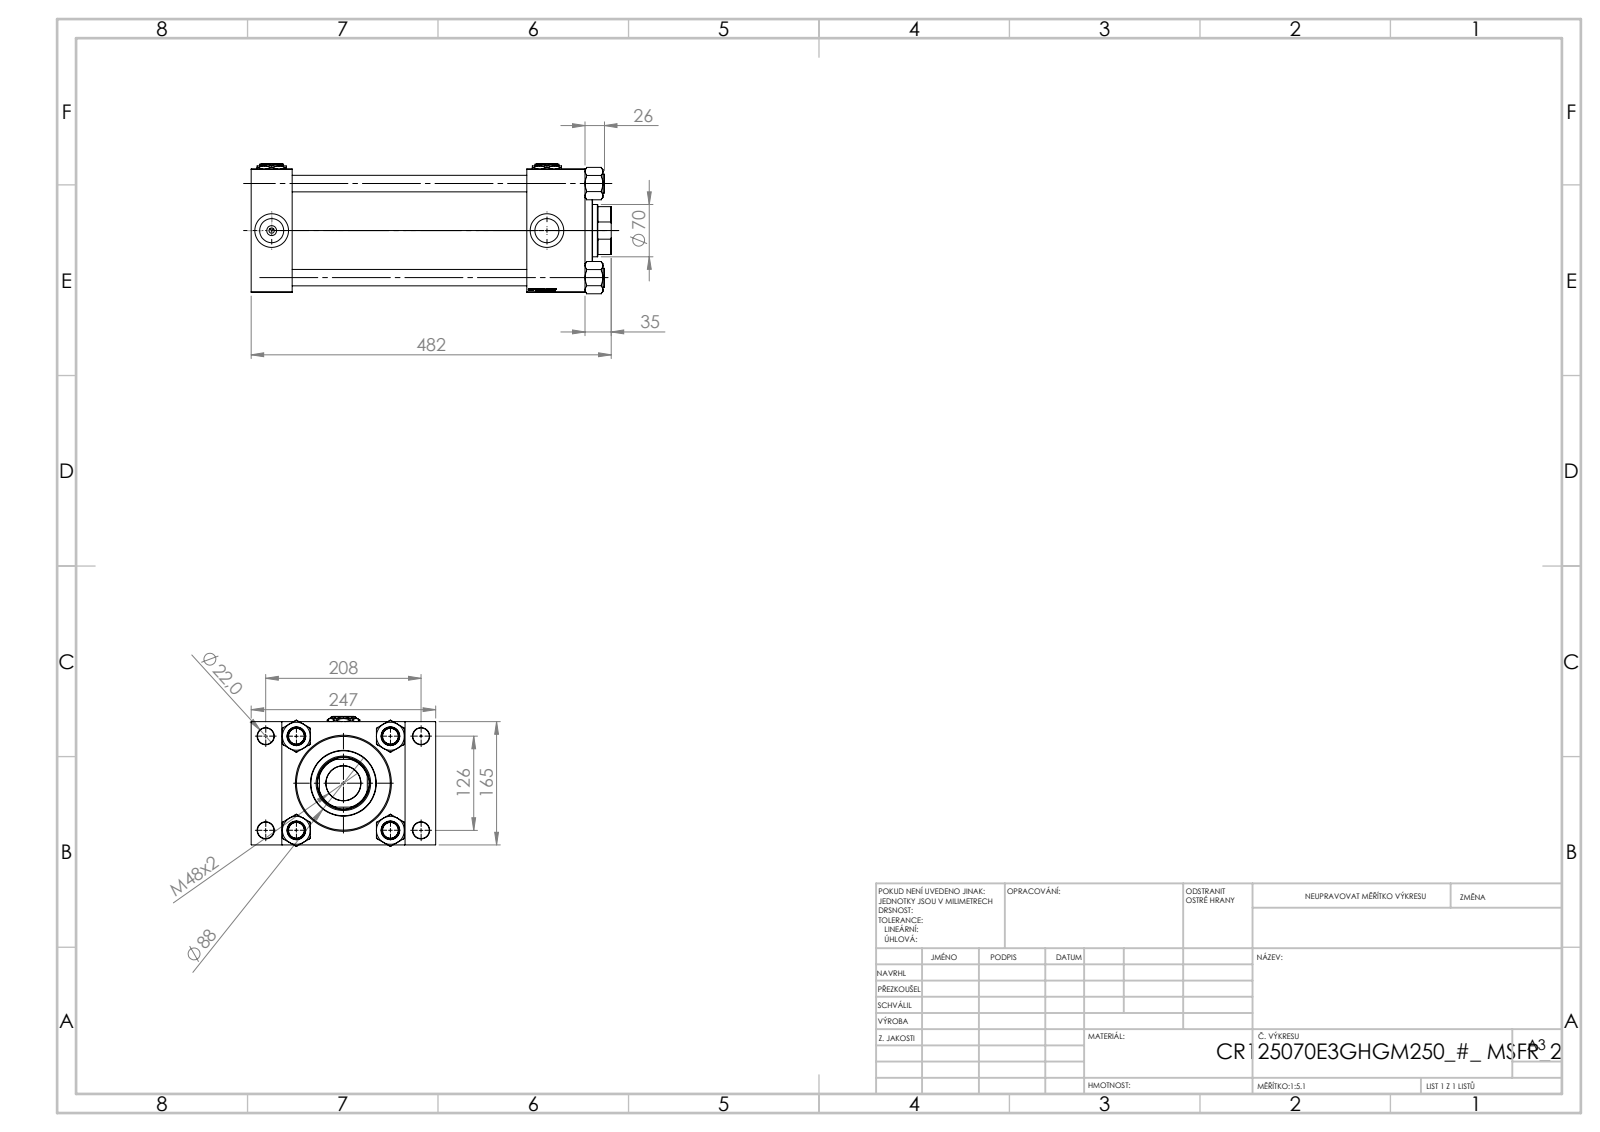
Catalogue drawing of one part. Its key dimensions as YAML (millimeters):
part_name: "NUT_M5_E; V215_VC_A; V215CR_VCP_E; V215CR_TYCINKA_E (+2 more)"
step_written_by: "SolidWorks 2019 (CONFIG_CONTROL_DESIGN)"
units: millimeters
bodies: {solids: 13, faces: 1290, planar: 595, cylindrical: 101, other: 594}
overall_size: [482, 247, 174.07]
volume: 6770000
surface_area: 890234
round_holes:
  - {diameter: 22, count: 8}
  - {diameter: 32.24, count: 4}
  - {diameter: 45, count: 4}
  - {diameter: 7, count: 3}
  - {diameter: 2.5, count: 2}
  - {diameter: 46.5, count: 1}
  - {diameter: 70, count: 1}
  - {diameter: 73, count: 1}
  - {diameter: 96, count: 1}
  - {diameter: 125, count: 1}
  - {diameter: 125.5, count: 1}
round_bosses_or_shafts:
  - {diameter: 25, count: 4}
  - {diameter: 131, count: 1}
  - {diameter: 88, count: 1}
partial_cylinders:
  - {radius: 34, count: 1}
face_to_face_distances: [55, 165, 447, 392, 41, 78, 369, 314, 206, 418.3]
hole_center_spacings: [41.05, 62.98, 76.28, 89.02, 121.59, 125.9, 132.47, 139.02]
